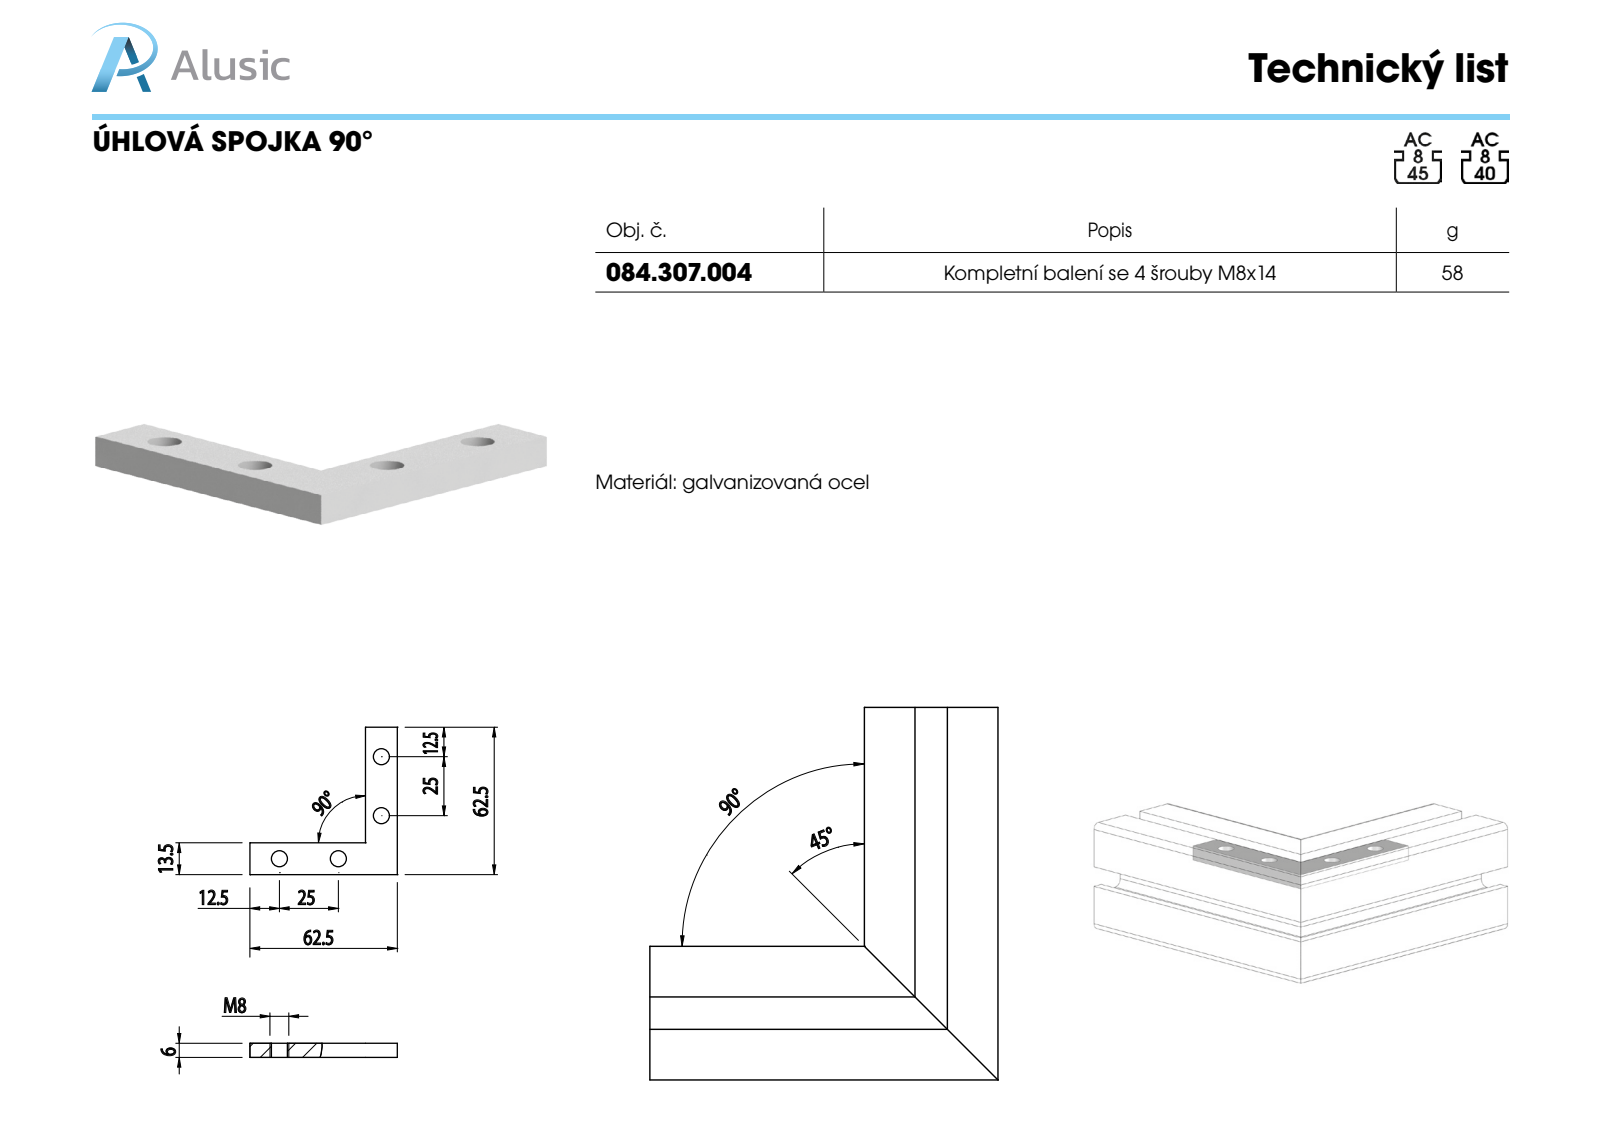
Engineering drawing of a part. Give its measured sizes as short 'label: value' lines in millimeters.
name: 084.307.004
written by: SolidWorks 2011 (CONFIG_CONTROL_DESIGN)
unit: mm
bodies: 1 solid, 16 faces (8 planar, 8 cylindrical, 0 other)
size: 62.5 × 62.5 × 6
volume: 8 160 mm³; area: 4 733 mm²
holes: 4× ⌀6.8
face distances: 6, 13.5, 49, 62.5
hole spacings: 25, 46.94, 25.81, 61.16
